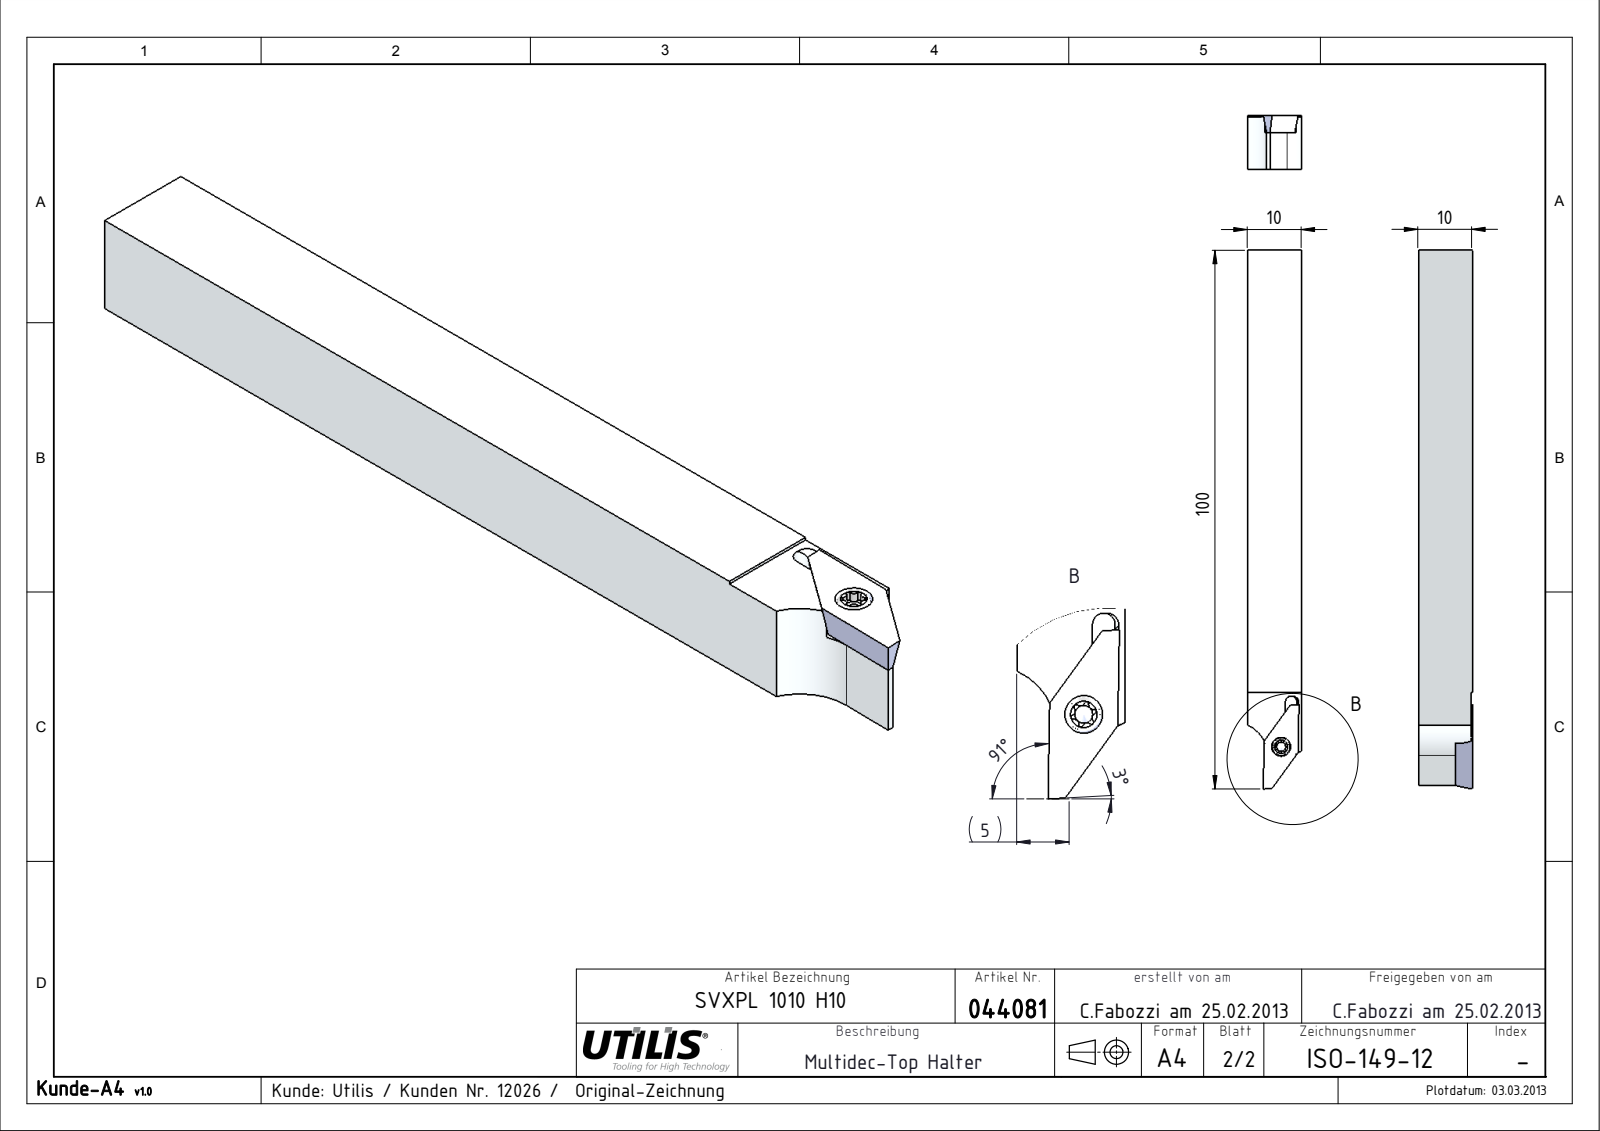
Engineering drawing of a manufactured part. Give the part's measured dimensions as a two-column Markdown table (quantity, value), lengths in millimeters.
| quantity | value |
| --- | --- |
| part name | ISO-149-Kunde_12; MSP-7_M2,5X6-TX8 CERATIZIT Schraube; ISO-149-12; VPGT 10 L_01 |
| STEP written by | SolidWorks 2015 (CONFIG_CONTROL_DESIGN) |
| units | millimeters |
| bodies | 3 solids, 71 faces (27 planar, 27 cylindrical, 17 other) |
| overall size | 100 × 10 × 10 |
| volume | 9 334 mm³ |
| surface area | 4 354 mm² |
| round holes (diameter × count) | 2.05 × 1, 3 × 1 |
| round bosses / shafts (diameter × count) | 3.45 × 1, 2.5 × 1 |
| partial cylindrical surfaces (radius × count) | 0.2 × 6, 0.45 × 6, 6 × 2, 1.05 × 1 |
| main face-to-face distances | 10, 6.82, 3.18, 9.7, 2.88, 5.33, 2.1, 3.23, 5.32, 82 |
